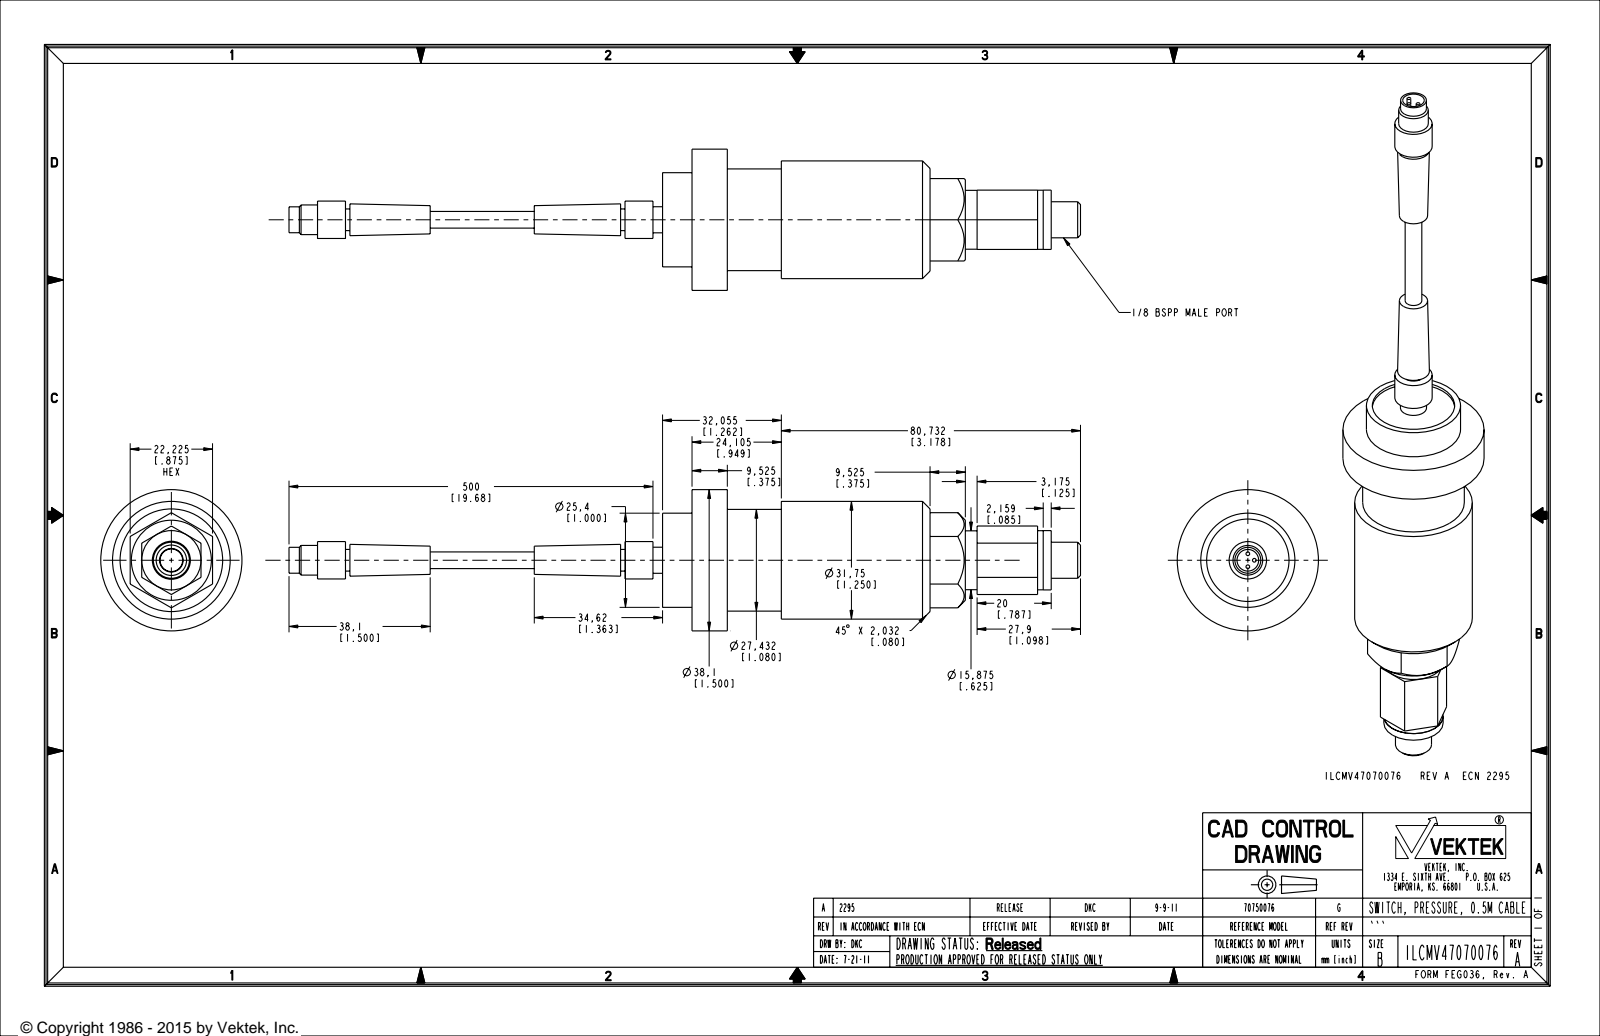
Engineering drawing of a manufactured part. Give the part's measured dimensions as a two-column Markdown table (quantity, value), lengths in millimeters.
| quantity | value |
| --- | --- |
| part name | ILCMV47070076 |
| STEP written by | PRO/ENGINEER BY PARAMETRIC TECHNOLOGY CORPORATION, 2007460 (AUTOMOTIVE_DESIGN_CC2) |
| units | millimeters |
| bodies | 1 solid, 103 faces (41 planar, 50 cylindrical, 12 other) |
| overall size | 213.6 × 38.1 × 38.1 |
| volume | 68 111 mm³ |
| surface area | 15 297 mm² |
| round holes (diameter × count) | 6.35 × 1, 10.26 × 1, 22.23 × 1 |
| round bosses / shafts (diameter × count) | 1 × 3, 38.1 × 1, 31.75 × 1, 27.43 × 1, 25.4 × 1, 16 × 1, 15.95 × 1, 15.88 × 1 |
| main face-to-face distances | 9.53, 3.11, 19.11, 16, 16.69, 7.16, 64.24, 22.22, 14.58, 24.11 |
